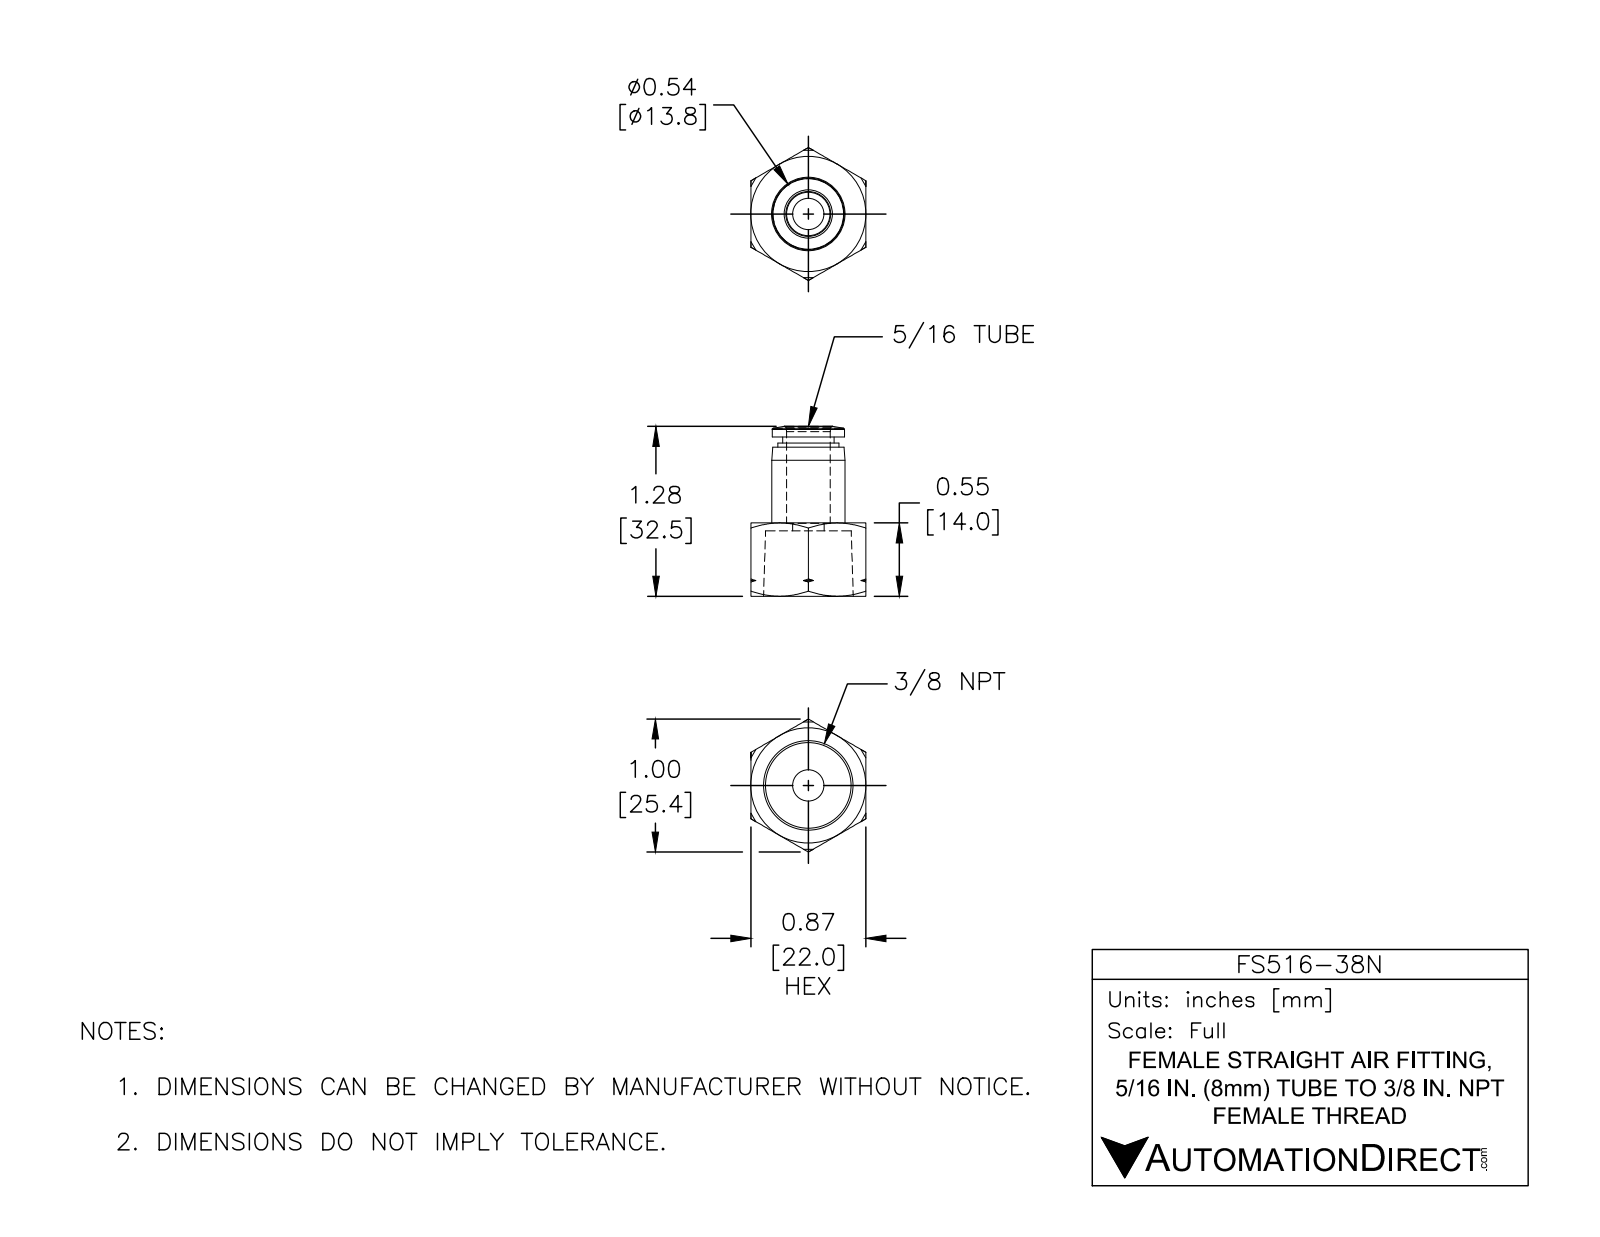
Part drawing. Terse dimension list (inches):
name: FS516-38N
written by: SolidWorks 2015 (CONFIG_CONTROL_DESIGN)
unit: in
bodies: 1 solid, 61 faces (13 planar, 12 cylindrical, 36 other)
size: 1.278 × 1 × 0.866
volume: 0.288 in³; area: 5.986 in²
holes: 1× ⌀0.236, 1× ⌀0.327
bosses: 1× ⌀0.551, 1× ⌀0.543, 1× ⌀0.461, 1× ⌀0.386
face distances: 0.866, 0.059, 0.492, 0.551, 1.199, 0.707, 0.648, 1.122, 0.63, 0.571
